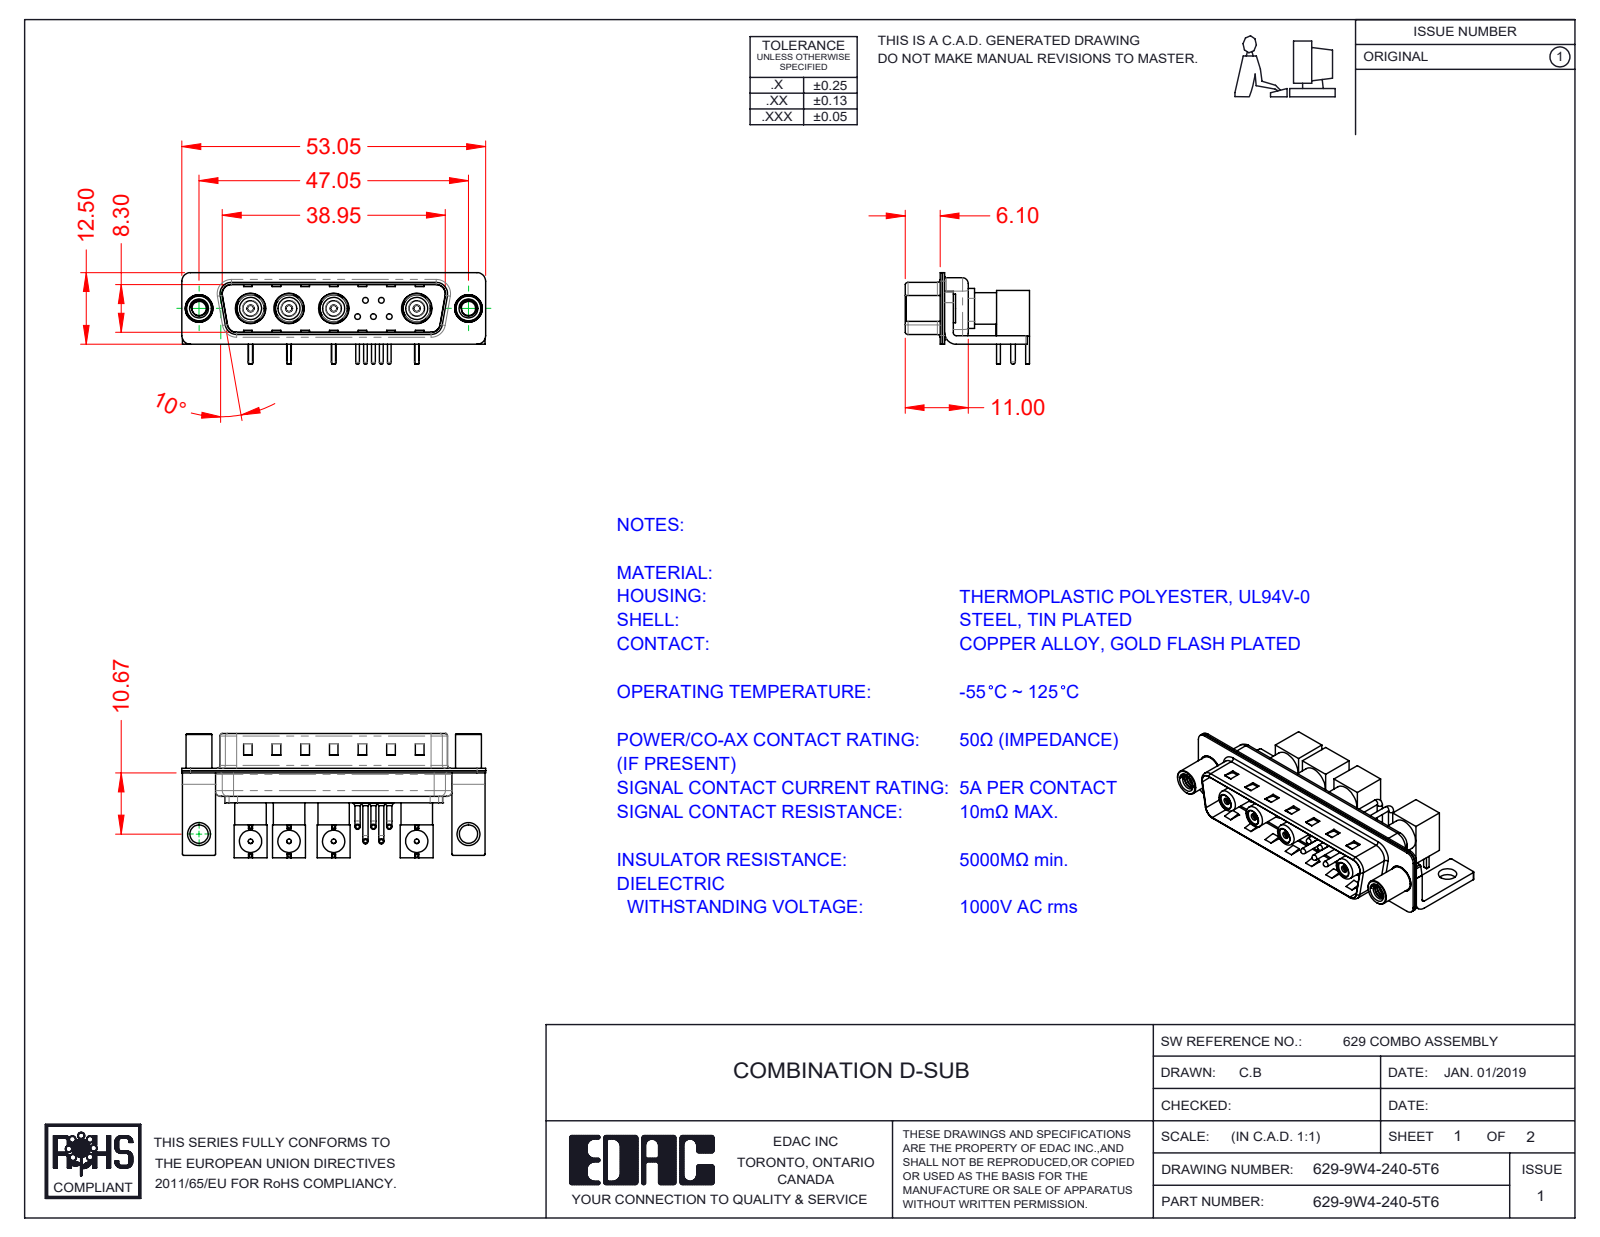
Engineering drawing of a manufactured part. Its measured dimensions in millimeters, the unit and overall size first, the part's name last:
Units: millimetres
Overall size (bounding box): 53.05 × 21.71 × 16
Round holes (diameter × count): ⌀1.6 ×9, ⌀2.5 ×6, ⌀0.75 ×5, ⌀2 ×5, ⌀0.8 ×4, ⌀1.1 ×4, ⌀1.2 ×4, ⌀1.5 ×4, ⌀2.7 ×4, ⌀3.1 ×4, ⌀3.4 ×4, ⌀3.9 ×4
Round bosses / shafts (diameter × count): ⌀0.9 ×10, ⌀0.8 ×8, ⌀1.5 ×5, ⌀1 ×5, ⌀0.65 ×5, ⌀5.5 ×4, ⌀5.2 ×4, ⌀4.8 ×4
Partial cylindrical surfaces — rounded edges, fillets, slot ends (radius × count): R0.25 ×16, R1.5 ×16, R2 ×13, R0.5 ×9, R1.6 ×8, R1.01 ×5, R0.6 ×4, R0.65 ×4
Main face-to-face distances: 0.4, 0.8, 9.5, 1.5, 5.75, 9.1, 8.7, 1.4, 9.9, 0.35
Hole centre spacings: 14.51, 14.52, 6.72, 7.79, 22.3, 29.02, 3.16, 14.5
Volume: 4 281 mm³ · Surface area: 11 553 mm²
Bodies: 40 solids, 1632 faces (741 planar, 657 cylindrical, 234 other)
Part name (STEP PRODUCT): 629Combo Shell Rear_25 Contacts; Insulator Socket; Co-Ax Jack Assy_RA; 629Combo Shell Front_25 Contacts (+8 more)
STEP written by: SolidWorks 2020 (CONFIG_CONTROL_DESIGN)
